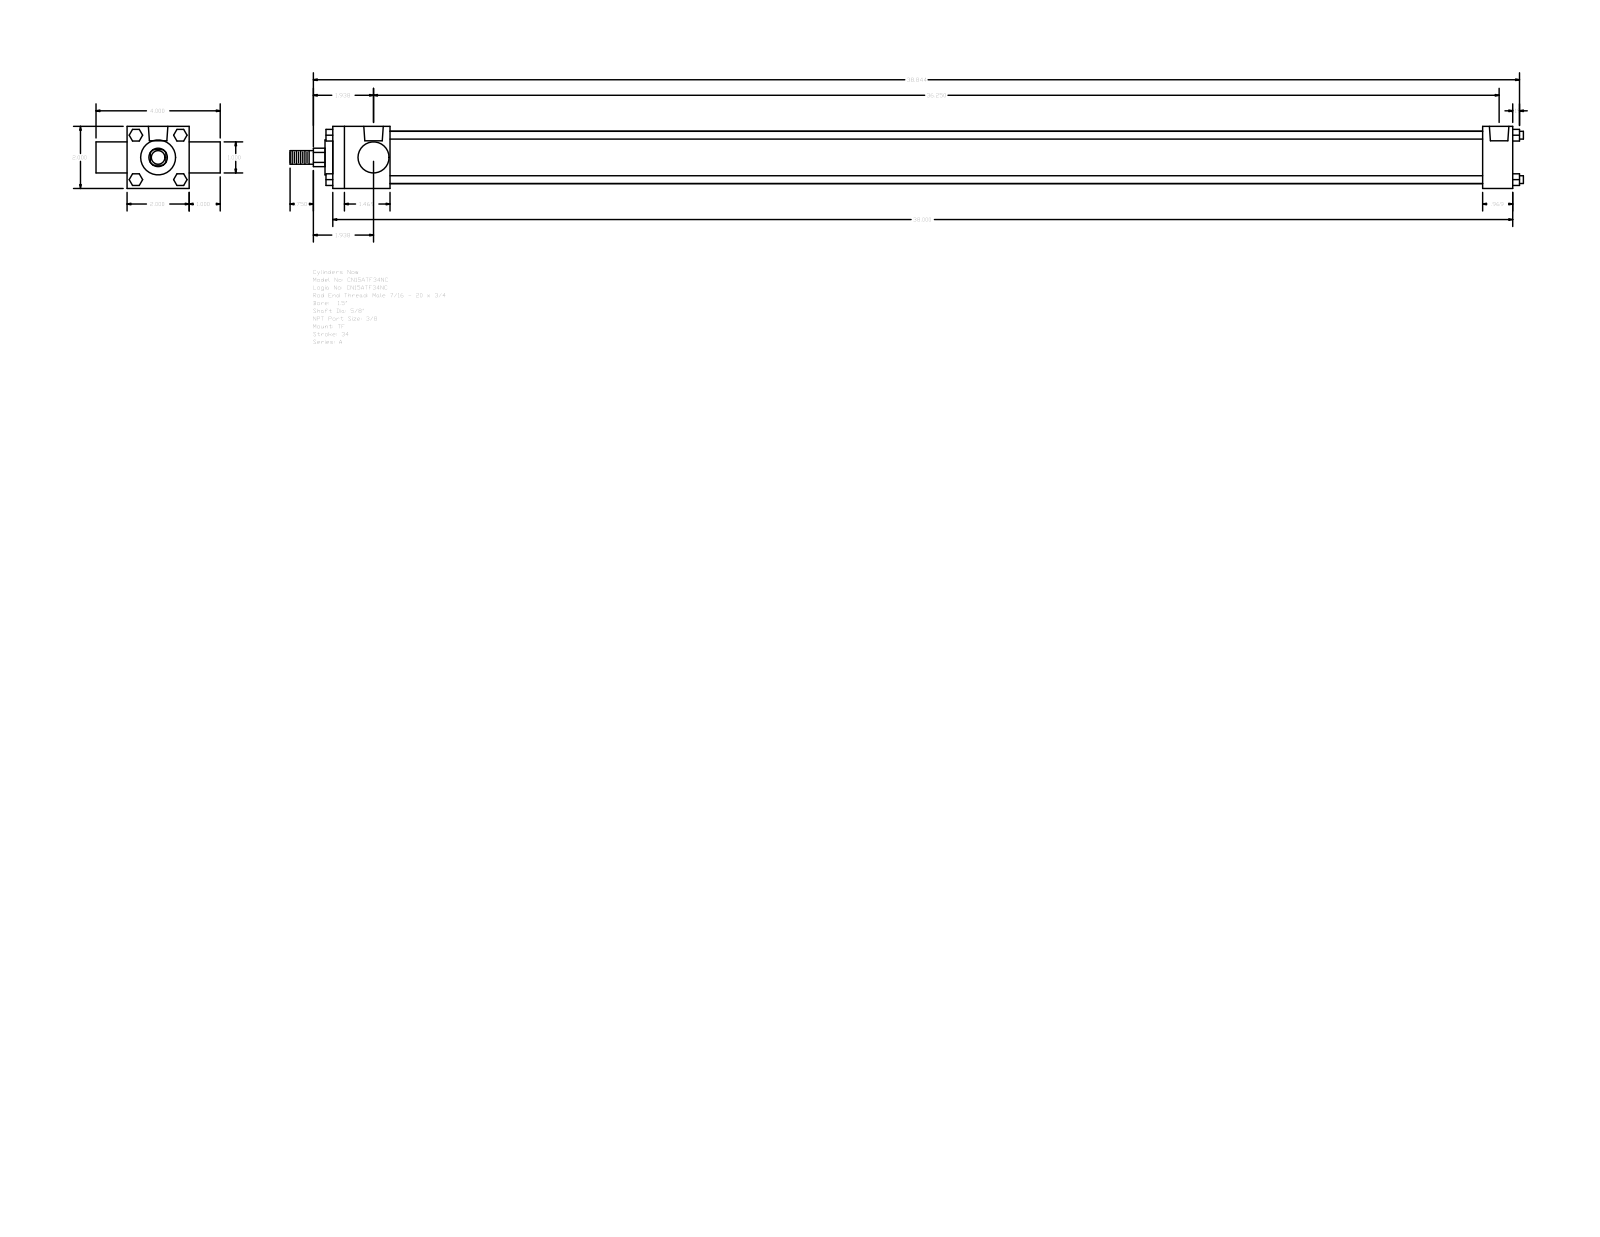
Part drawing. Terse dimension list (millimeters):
name: A_TF__0150_0.625
written by: GSSL Pune (CONFIG_CONTROL_DESIGN)
unit: mm
bodies: 0 solids, 120 faces (92 planar, 28 cylindrical, 0 other)
size: 1008.86 × 101.6 × 50.8
holes: 3× ⌀5.56, 2× ⌀15.93
bosses: 4× ⌀6.35, 1× ⌀42.93, 1× ⌀28.57, 1× ⌀25.4, 1× ⌀15.88, 1× ⌀11.11
rounds: 1× R7.54
face distances: 50.8, 965.2, 25.4, 76.2, 46.83, 940.59, 893.76, 918.37, 24.61, 101.6
hole spacings: 3.97, 916.78, 912.81, 920.75
